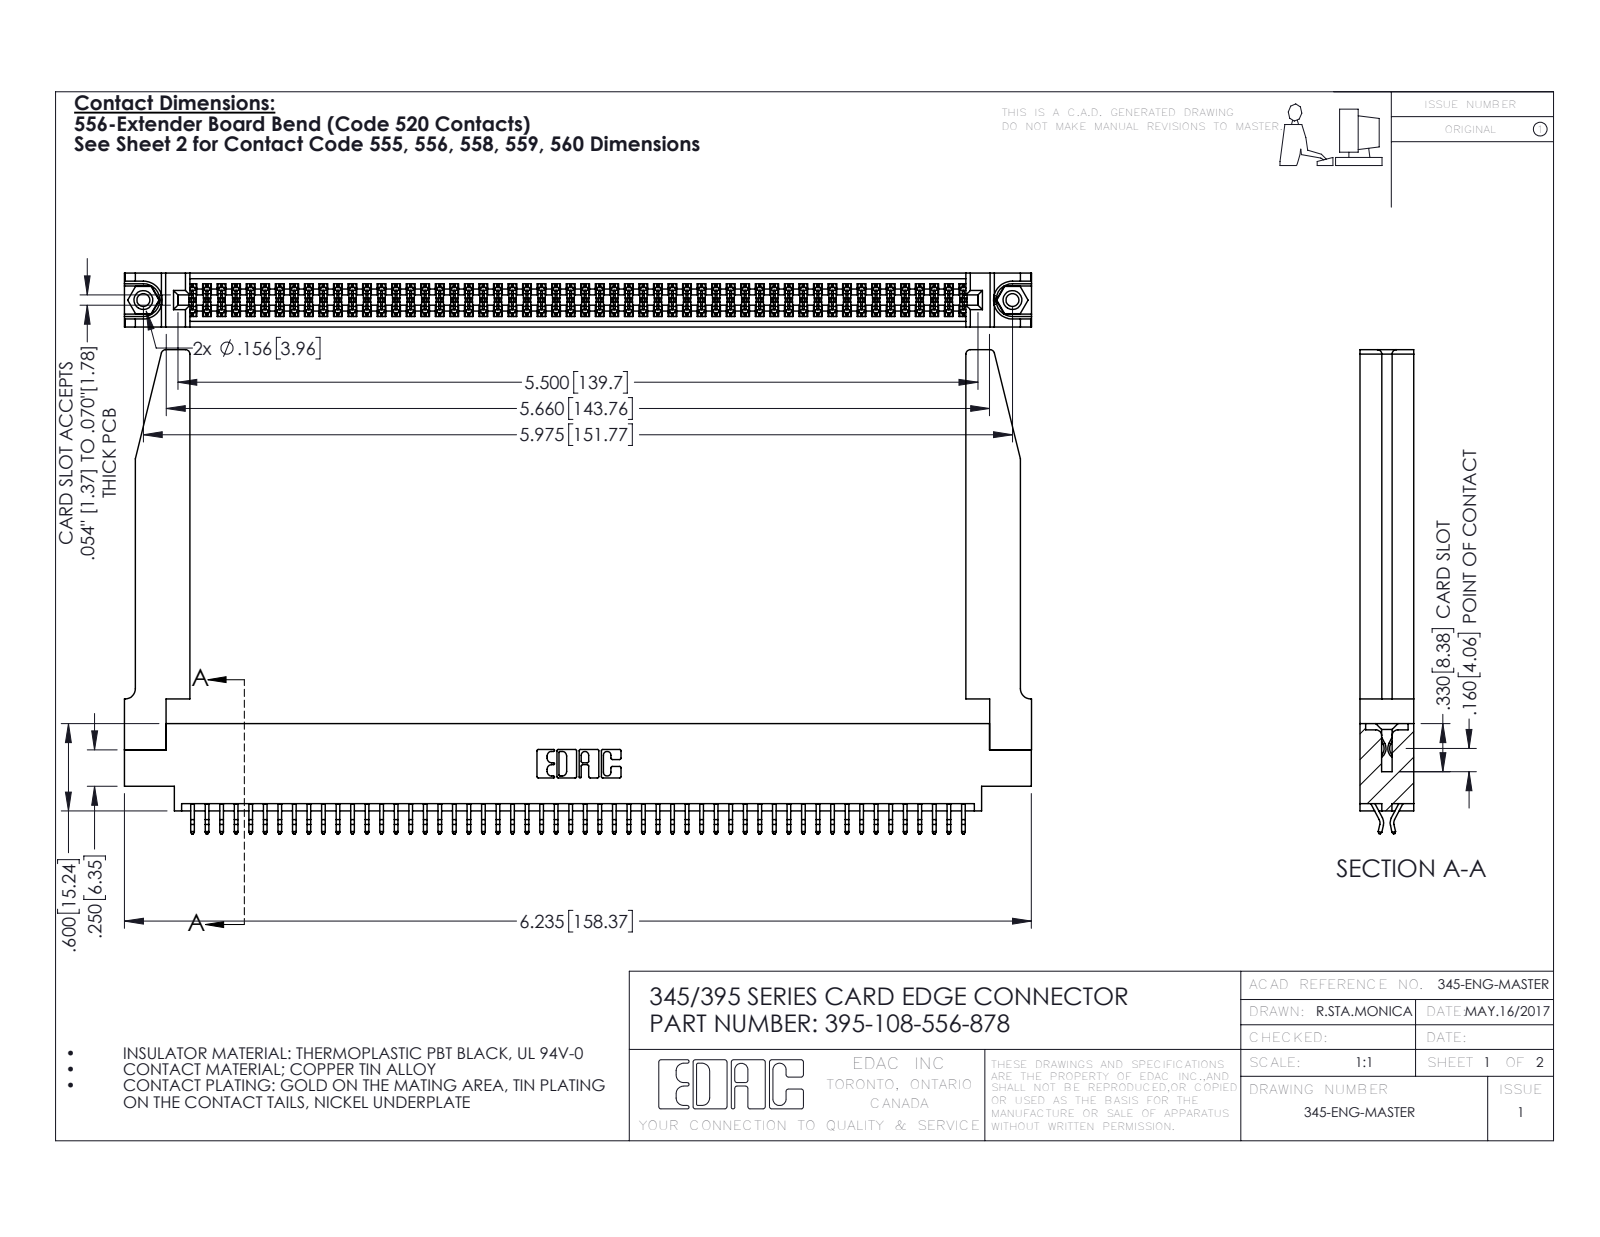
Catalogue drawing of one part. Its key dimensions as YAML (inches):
part_name: "345 Part_0.170 Offset - 0.156 Dia-TH; 395-108-556-878; 345-292-001_556 Tail; 345-250-001_345-250-001-102 (+1 more)"
step_written_by: "SolidWorks 2016 (CONFIG_CONTROL_DESIGN)"
units: inches
bodies: {solids: 113, faces: 6412, planar: 4222, cylindrical: 2138, other: 52}
overall_size: [6.236, 3.327, 0.37]
volume: 1.413
surface_area: 46.27
round_holes:
  - {diameter: 0.089, count: 2}
  - {diameter: 0.125, count: 2}
  - {diameter: 0.156, count: 2}
  - {diameter: 0.064, count: 1}
round_bosses_or_shafts:
  - {diameter: 0.155, count: 2}
partial_cylinders:
  - {radius: 0.006, count: 162}
  - {radius: 0.01, count: 22}
  - {radius: 0.03, count: 8}
  - {radius: 0.007, count: 6}
  - {radius: 0.031, count: 6}
  - {radius: 0.026, count: 3}
  - {radius: 0.01, count: 2}
  - {radius: 0.014, count: 2}
face_to_face_distances: [0.37, 0.072, 0.298, 0.025, 0.098, 0.272, 0.2, 0.225, 0.175, 0.148]
hole_center_spacings: [0.27, 5.739, 5.975]
